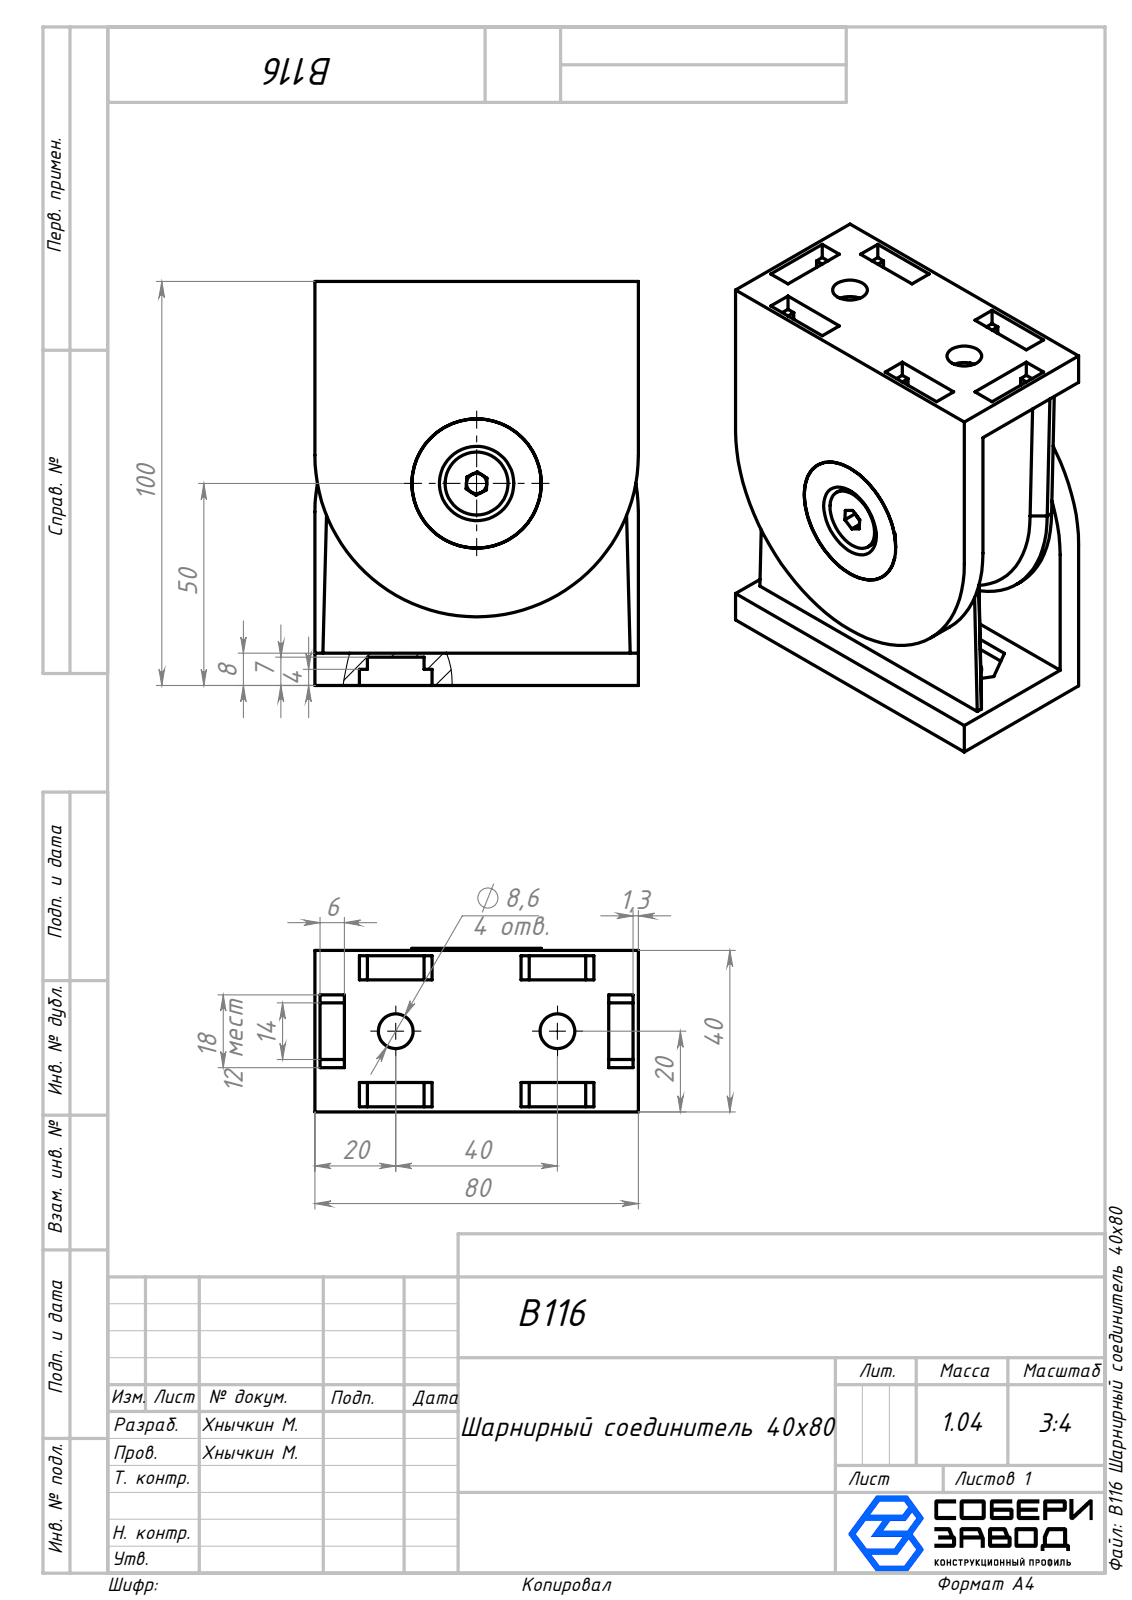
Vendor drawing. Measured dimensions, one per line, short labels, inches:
name: B116 Половины корпуса_00; socket countersunk head screw_din_DIN 7991 - M8 x 16 --- 16N; B116 Шарнирный соединитель 40х80; B116 Соединение_00
written by: SolidWorks 2026 (AUTOMOTIVE_DESIGN)
unit: in
bodies: 6 solids, 342 faces (250 planar, 52 cylindrical, 40 other)
size: 4.173 × 3.15 × 1.654
volume: 10.05 in³; area: 110.7 in²
holes: 4× ⌀0.339, 1× ⌀0.276
bosses: 1× ⌀0.787, 1× ⌀0.613, 1× ⌀0.315
rounds: 2× R1.457, 2× R1.575, 1× R0.236
face distances: 0.256, 1.24, 0.984, 1.063, 0.177, 0.433, 0.807, 1.496, 0.63, 0.315
hole spacings: 0.079, 1.575, 1.577
